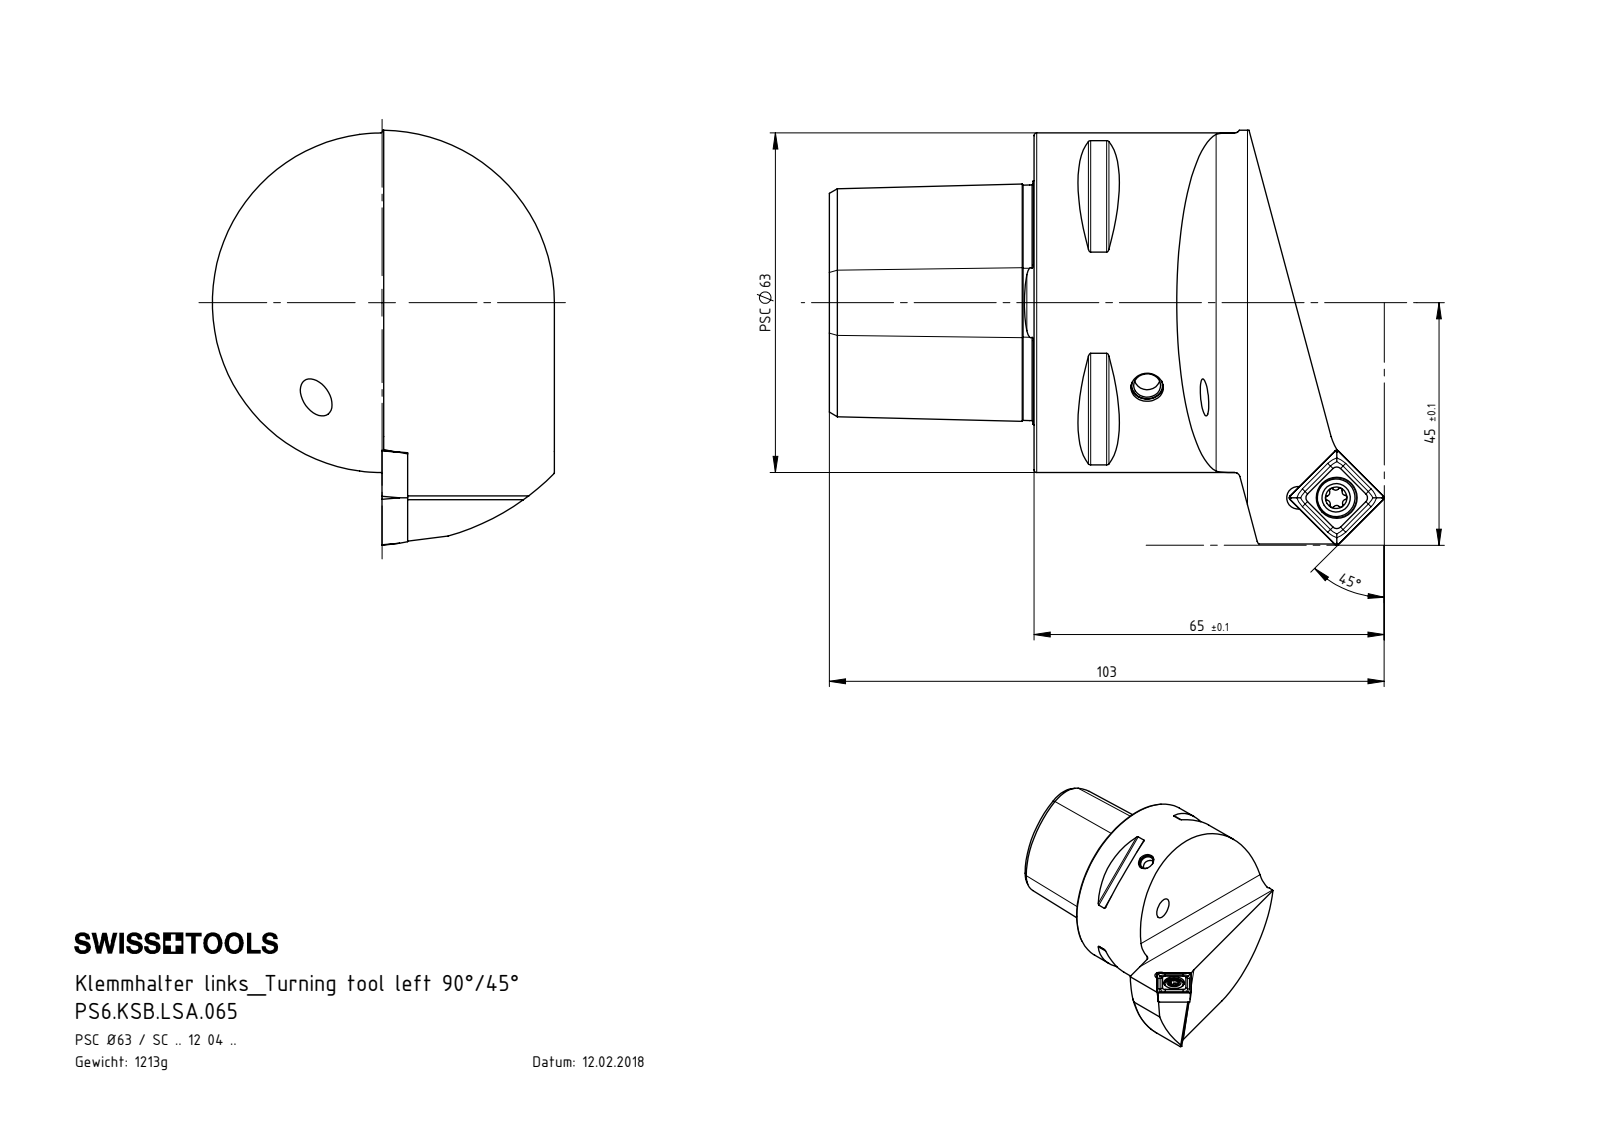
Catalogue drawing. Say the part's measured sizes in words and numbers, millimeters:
The part is named "KVT_MB_600_060; PS6.KSB.LSA.065; SCMT120404; PS6-KSB.LSA.065_A_Fertigbearbeitung (+1 more)". Its 3-D file was written by "SolidWorks 2017 (AUTOMOTIVE_DESIGN)". It is 5 solids with 269 faces: 51 planar, 68 cylindrical and 150 other. Overall it measures 103 by 77 by 63.5 millimeters. Its volume is 154 541 cubic millimeters and its surface area 28 138 square millimeters. Round holes: 2 of diameter 4.2, 2 of diameter 5, 1 of diameter 4, 1 of diameter 5.5, 1 of diameter 7.6, 1 of diameter 8.1, 1 of diameter 18, 1 of diameter 28, 1 of diameter 32. Round bosses or shafts: 1 of diameter 63, 1 of diameter 7, 1 of diameter 6, 1 of diameter 5. Partial cylindrical surfaces (rounded edges, fillets, slot ends): 8 of radius 0.5, 6 of radius 0.39, 3 of radius 0.69, 3 of radius 0.69, 2 of radius 6, 1 of radius 9, 1 of radius 32, 1 of radius 45. The main face-to-face distances are 38, 31.7, 24.88, 27, 11, 27.24, 4.46, 55.8, 37.8, 10.8. The hole center spacings are 7.07, 7.18, 27.5, 51.76, 57.03, 57.12, 73.97, 80.21.
